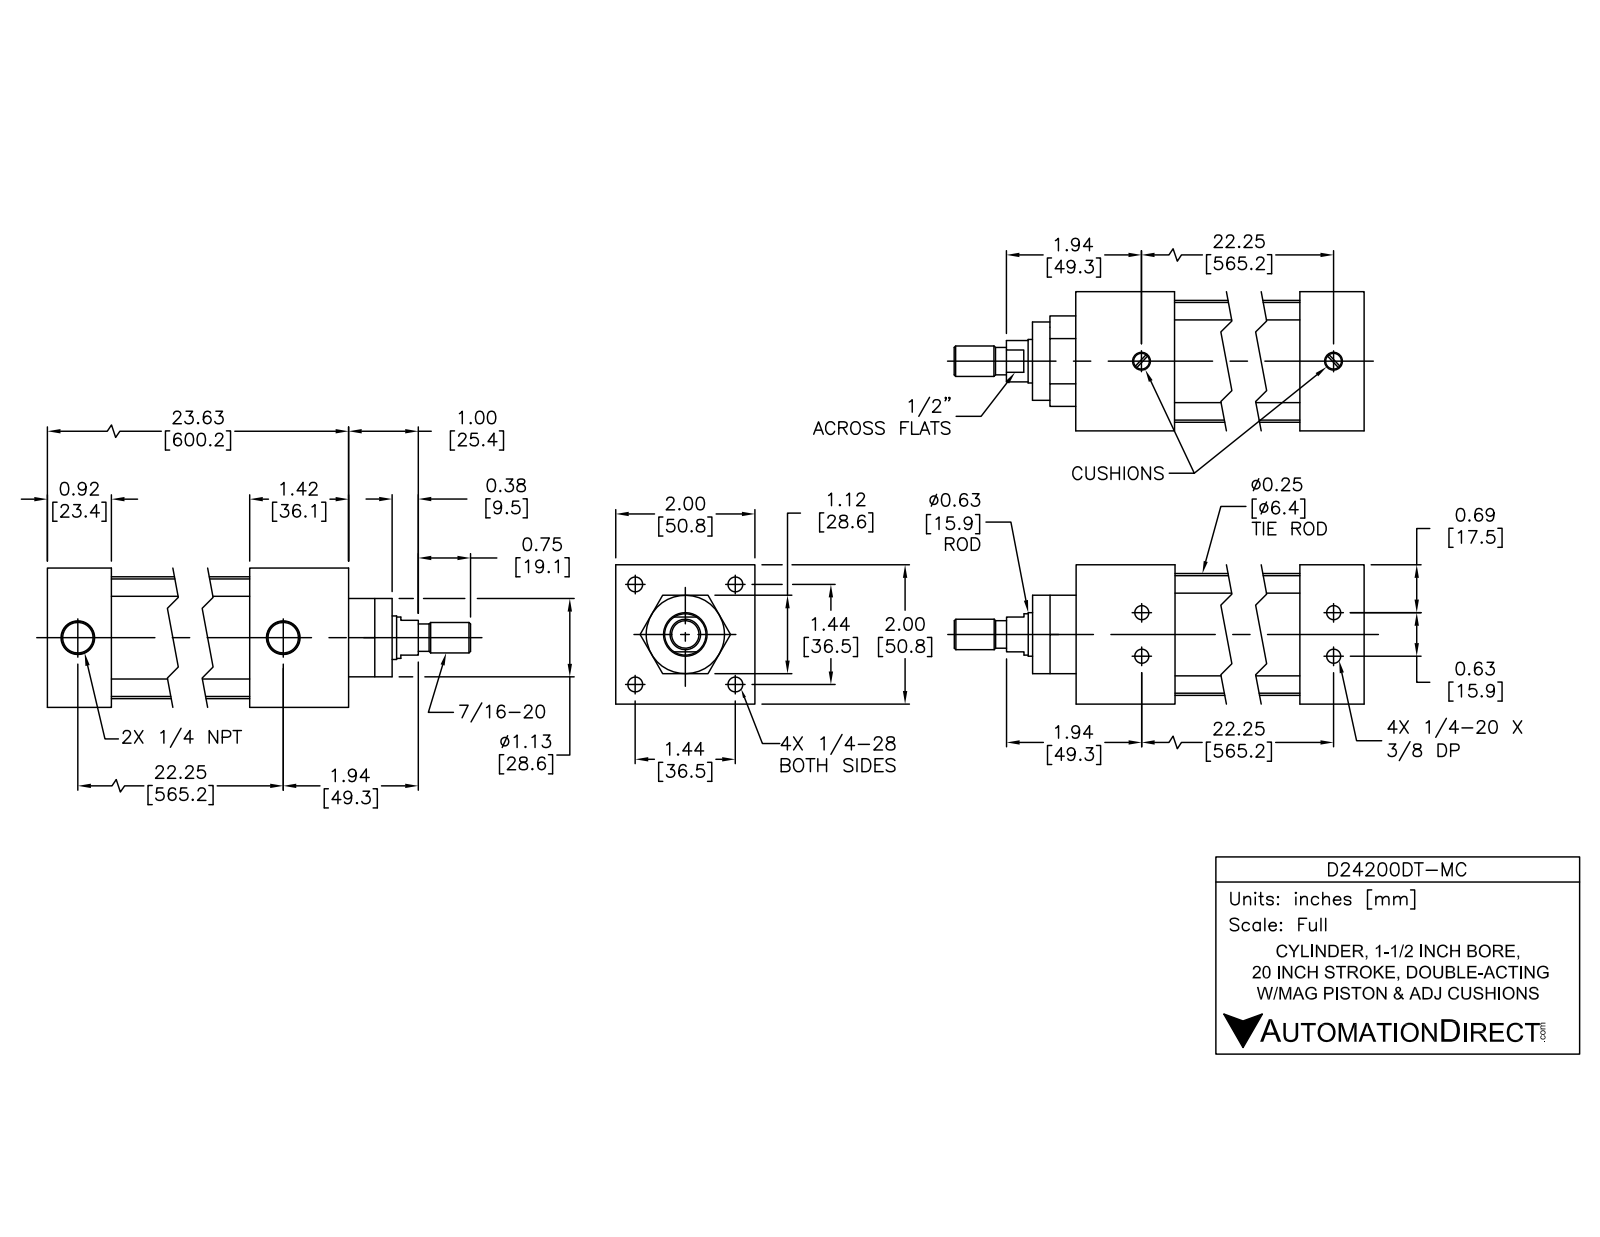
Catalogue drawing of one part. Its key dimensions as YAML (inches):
part_name: "D24200DT-M BODY; D24200DT-MC; D24200DT-M PISTON"
step_written_by: "SolidWorks 2015 (AUTOMOTIVE_DESIGN)"
units: inches
bodies: {solids: 12, faces: 303, planar: 99, cylindrical: 114, other: 90}
overall_size: [25.371, 2, 2]
volume: 34.63
surface_area: 392.1
round_holes:
  - {diameter: 0.196, count: 4}
  - {diameter: 0.211, count: 4}
  - {diameter: 0.281, count: 4}
  - {diameter: 0.406, count: 4}
  - {diameter: 0.297, count: 2}
  - {diameter: 0.477, count: 2}
  - {diameter: 0.625, count: 1}
  - {diameter: 0.628, count: 1}
  - {diameter: 1.5, count: 1}
round_bosses_or_shafts:
  - {diameter: 0.39, count: 4}
  - {diameter: 0.25, count: 4}
  - {diameter: 0.222, count: 4}
  - {diameter: 1.75, count: 1}
  - {diameter: 1.497, count: 1}
  - {diameter: 1.121, count: 1}
  - {diameter: 0.622, count: 1}
  - {diameter: 0.59, count: 1}
partial_cylinders:
  - {radius: 0.2, count: 4}
face_to_face_distances: [2, 23.621, 1.42, 22.201, 22.701, 21.281, 0.92, 1.121, 22.601, 21.181]
hole_center_spacings: [0.313, 1.014, 1.434, 0.625, 2.028, 22.247, 22.248, 22.248]
